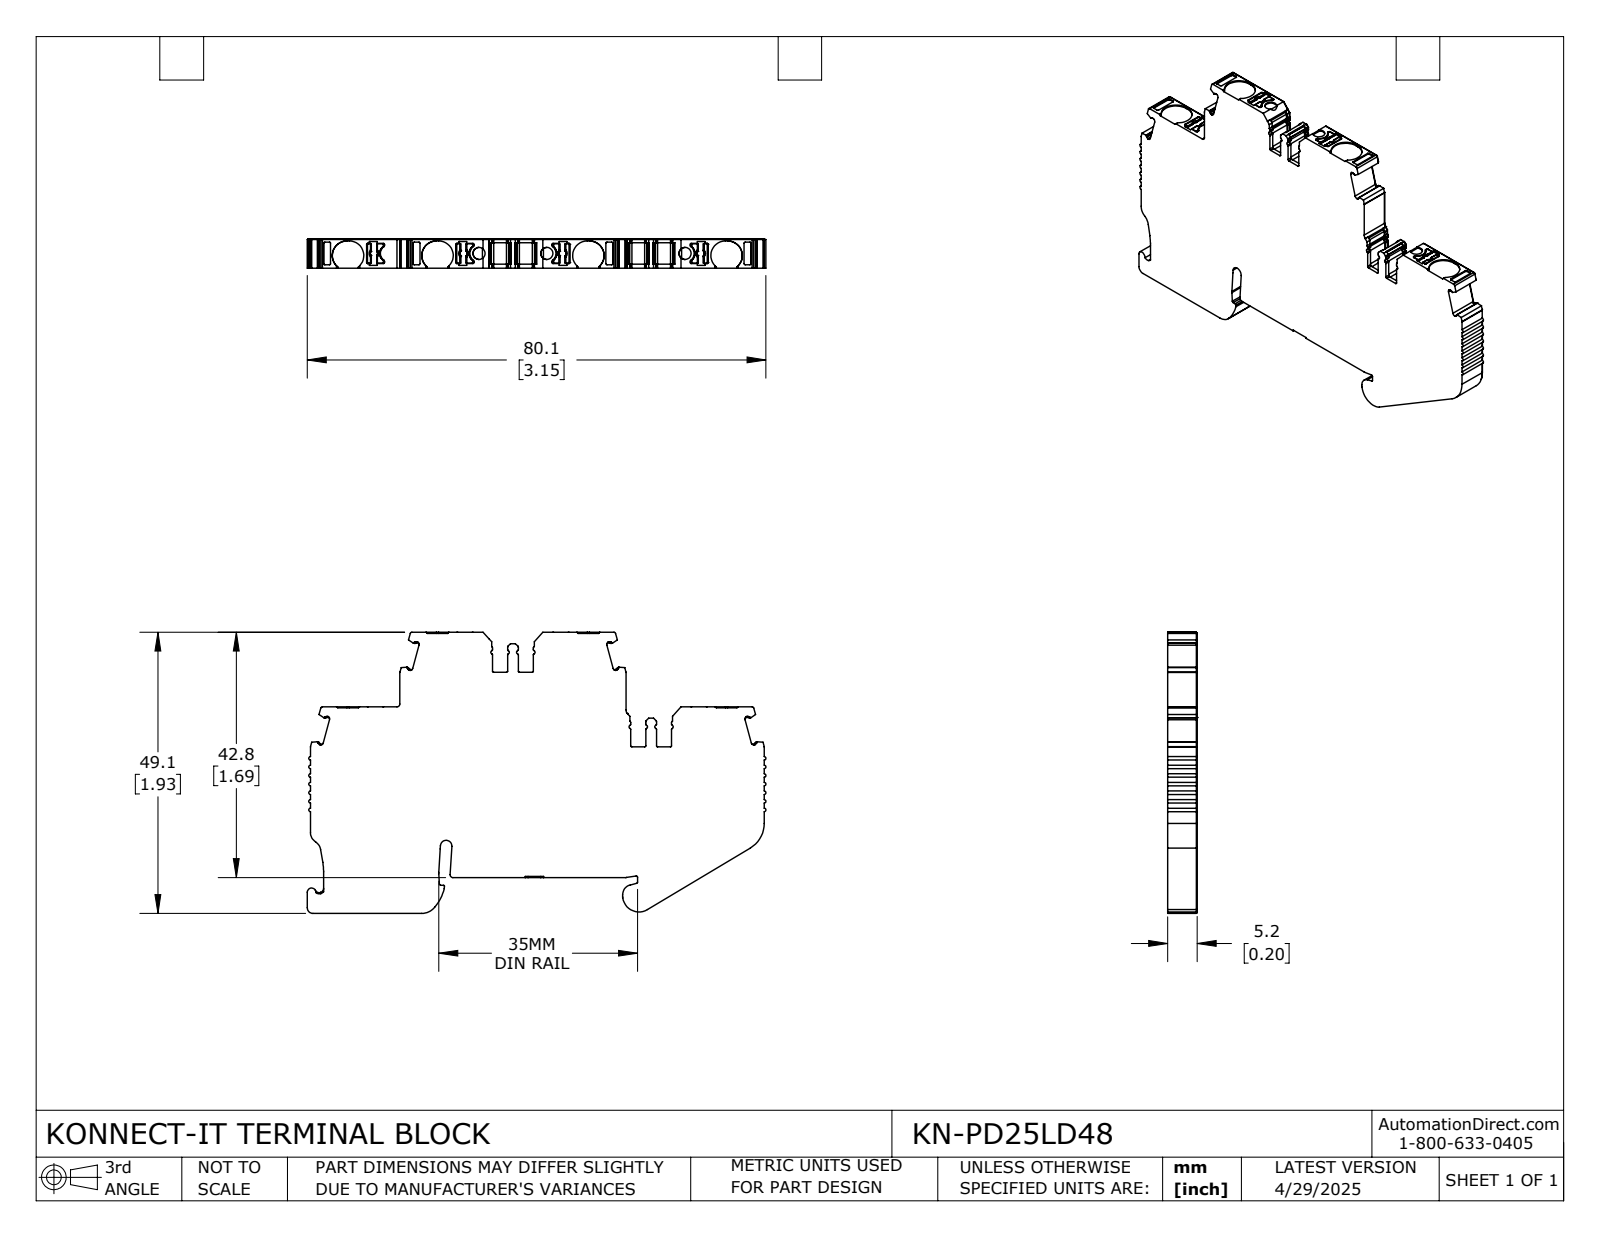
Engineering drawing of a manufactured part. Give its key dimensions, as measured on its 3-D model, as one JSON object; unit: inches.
{"part_name": "KN-PD25LD48", "step_written_by": "SolidWorks 2024 (CONFIG_CONTROL_DESIGN)", "units": "inches", "bodies": {"solids": 1, "faces": 979, "planar": 470, "cylindrical": 438, "other": 71}, "overall_size": [3.153, 1.933, 0.203], "volume_in3": 0.889, "surface_area_in2": 11.63, "round_holes": [[0.083, 3]], "partial_cylinders_radius": [[0.008, 100], [0.012, 57], [0.004, 41], [0.02, 21], [0.016, 17], [0.006, 16], [0.024, 9], [0.006, 8]], "face_to_face_distances": [0.203, 0.512, 0.246, 1.678, 1.166, 1.924, 0.079, 1.412, 0.504, 0.95], "hole_center_spacings": [0.466, 0.95, 1.417]}
